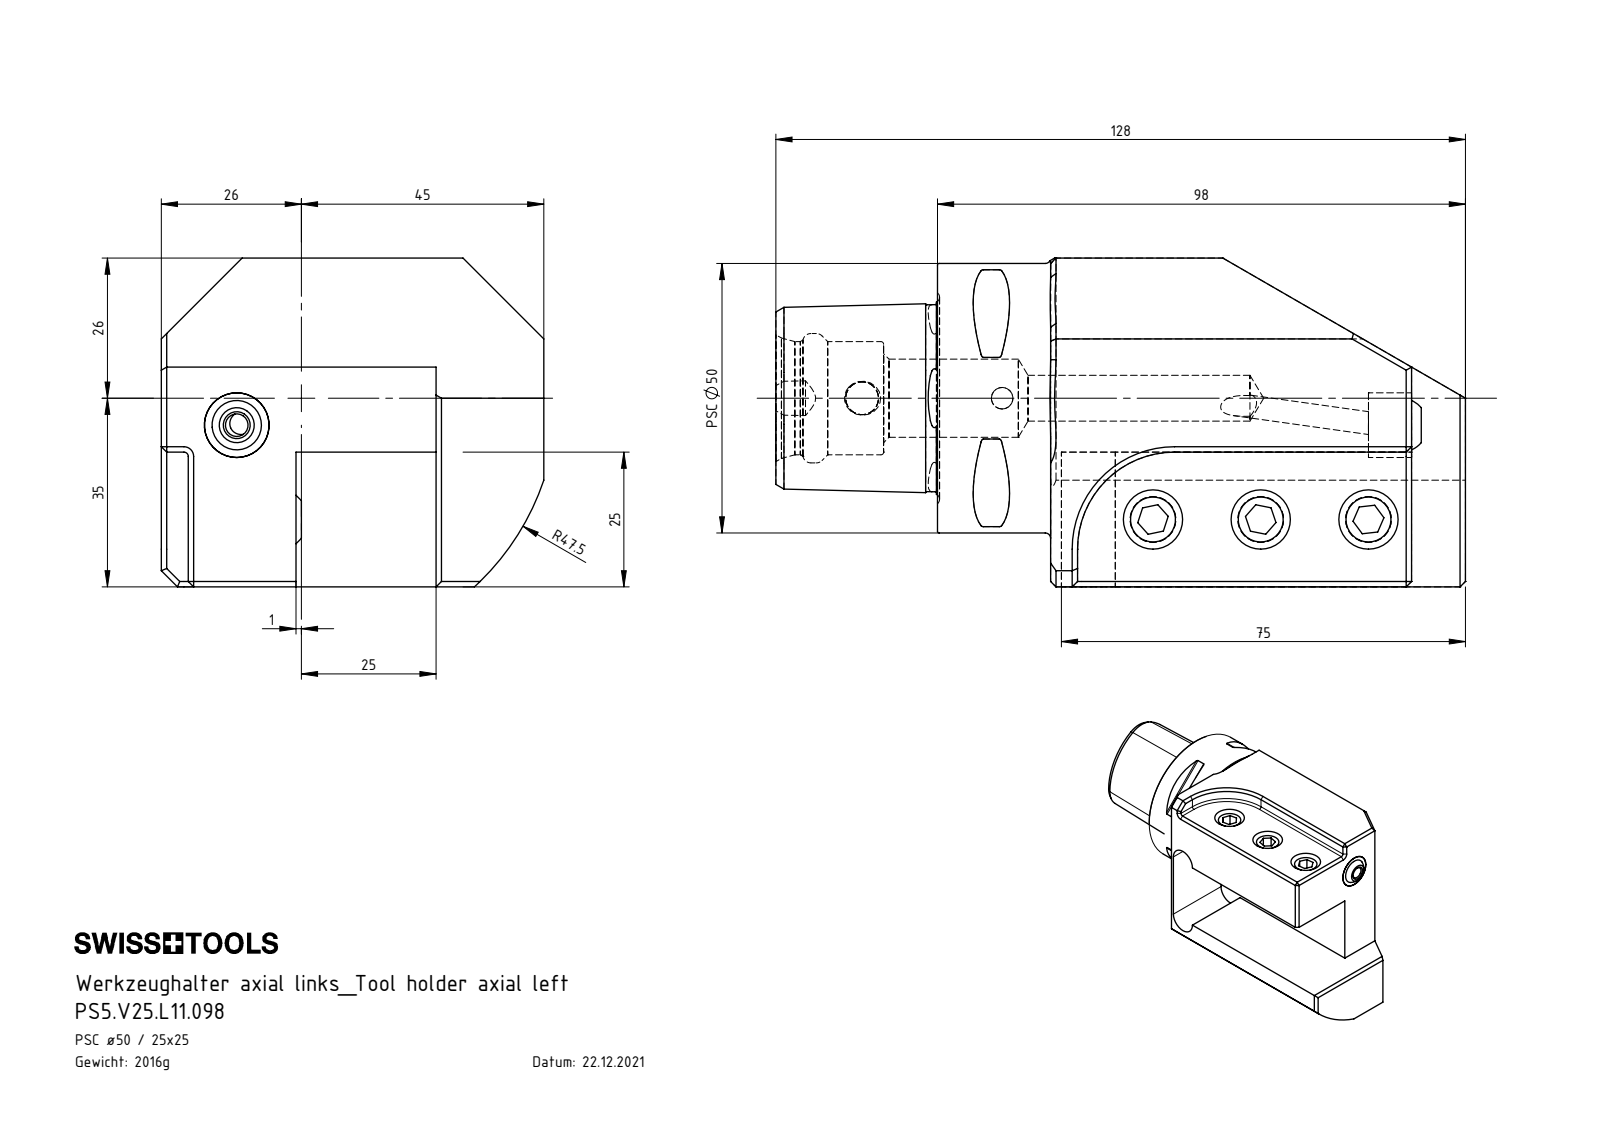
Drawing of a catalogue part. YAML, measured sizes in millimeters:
part_name: "KU1-U12.001.010; PS5.V25.L11.098; ISO 4026 - M10 x 20; PS5-V25.L11.098_A (+2 more)"
step_written_by: "SolidWorks 2017 (AUTOMOTIVE_DESIGN)"
units: millimeters
bodies: {solids: 6, faces: 197, planar: 92, cylindrical: 35, other: 70}
overall_size: [128, 71, 61]
volume: 257023
surface_area: 42525
round_holes:
  - {diameter: 8.5, count: 4}
  - {diameter: 4.2, count: 2}
  - {diameter: 4, count: 1}
  - {diameter: 6.1, count: 1}
  - {diameter: 7, count: 1}
  - {diameter: 12, count: 1}
  - {diameter: 14.5, count: 1}
  - {diameter: 21, count: 1}
  - {diameter: 24, count: 1}
round_bosses_or_shafts:
  - {diameter: 10, count: 3}
  - {diameter: 50, count: 1}
partial_cylinders:
  - {radius: 0.5, count: 8}
  - {radius: 0.8, count: 2}
  - {radius: 5, count: 2}
  - {radius: 4, count: 1}
  - {radius: 18, count: 1}
  - {radius: 47.5, count: 1}
face_to_face_distances: [25, 20, 46, 51, 71, 26, 36, 61, 5, 67]
hole_center_spacings: [20, 13, 26, 35.92, 40, 53.01, 58.5, 71.63]
